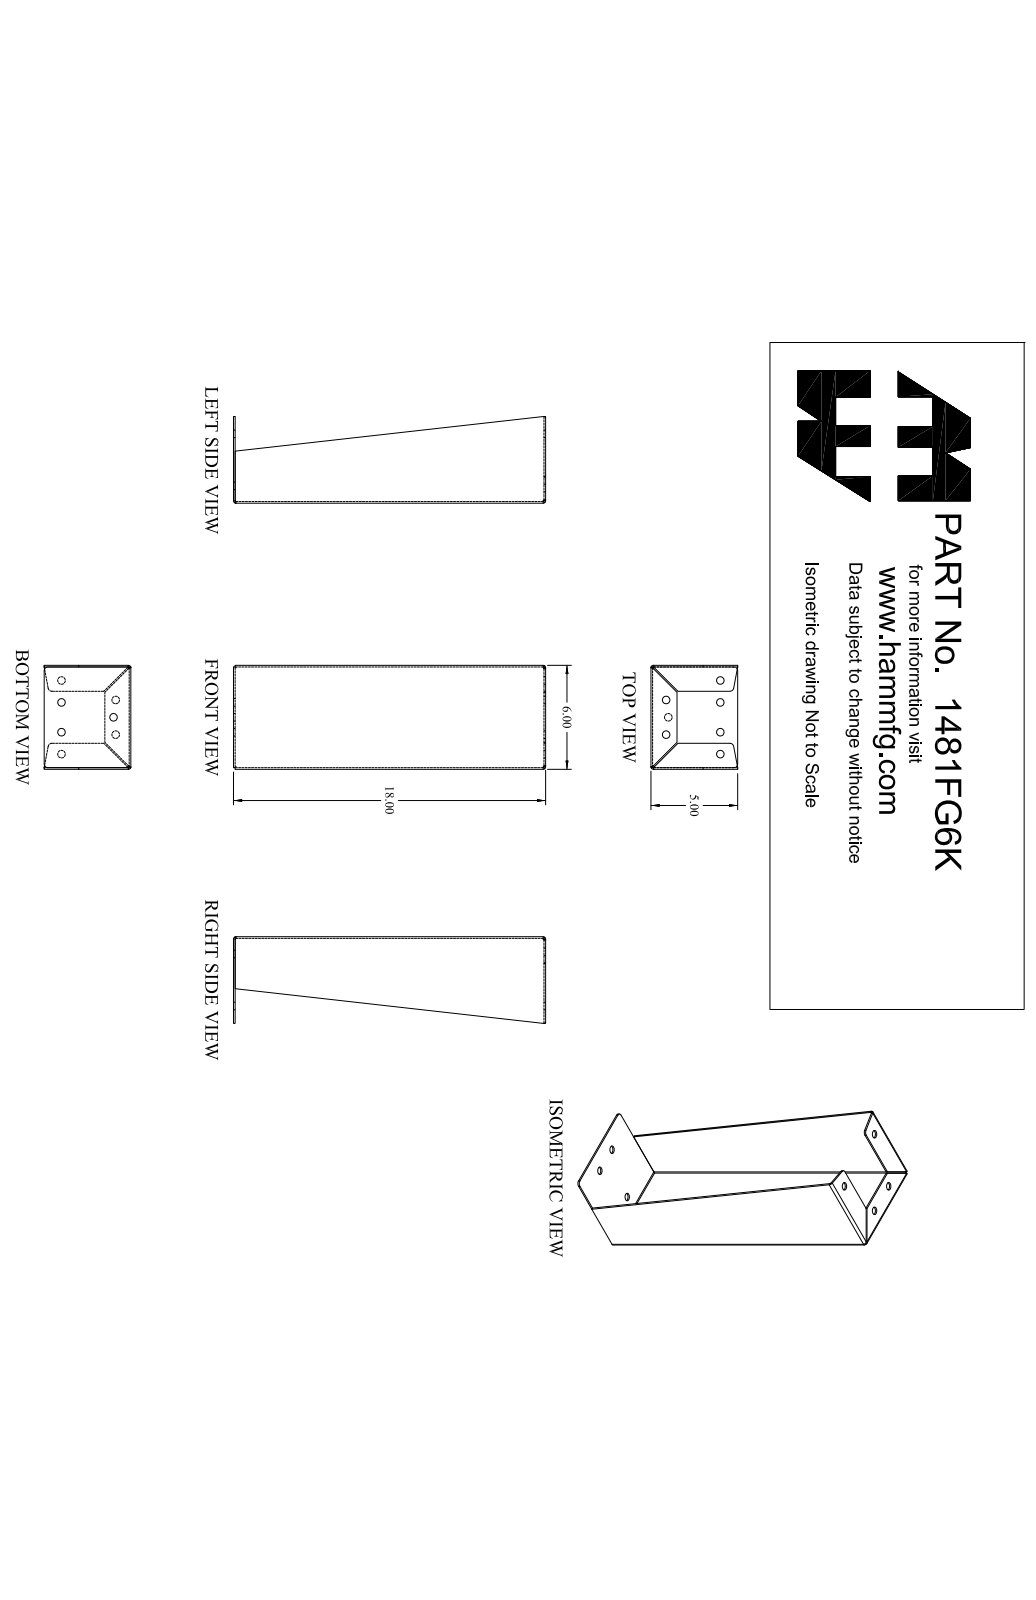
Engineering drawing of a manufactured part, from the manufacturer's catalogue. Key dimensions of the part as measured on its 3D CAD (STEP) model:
Part name (STEP PRODUCT): 1481FG6K_Default
STEP written by: SolidWorks 2019 (CONFIG_CONTROL_DESIGN)
Units: inches
Bodies: 1 solid, 78 faces (42 planar, 30 cylindrical, 6 other)
Overall size (bounding box): 18 × 6 × 5
Volume: 27.6 in³ · Surface area: 589.3 in²
Round holes (diameter × count): ⌀0.437 ×7
Partial cylindrical surfaces — rounded edges, fillets, slot ends (radius × count): R0.048 ×6, R0.143 ×6, R0.22 ×4
Main face-to-face distances: 0.095, 5.905, 5.81, 6, 0.095, 17.81, 17.905, 17.905, 18, 1.405
Hole centre spacings: 1.008, 3.12, 3.128, 3.321, 3.636, 4.419, 1.266, 1.266
